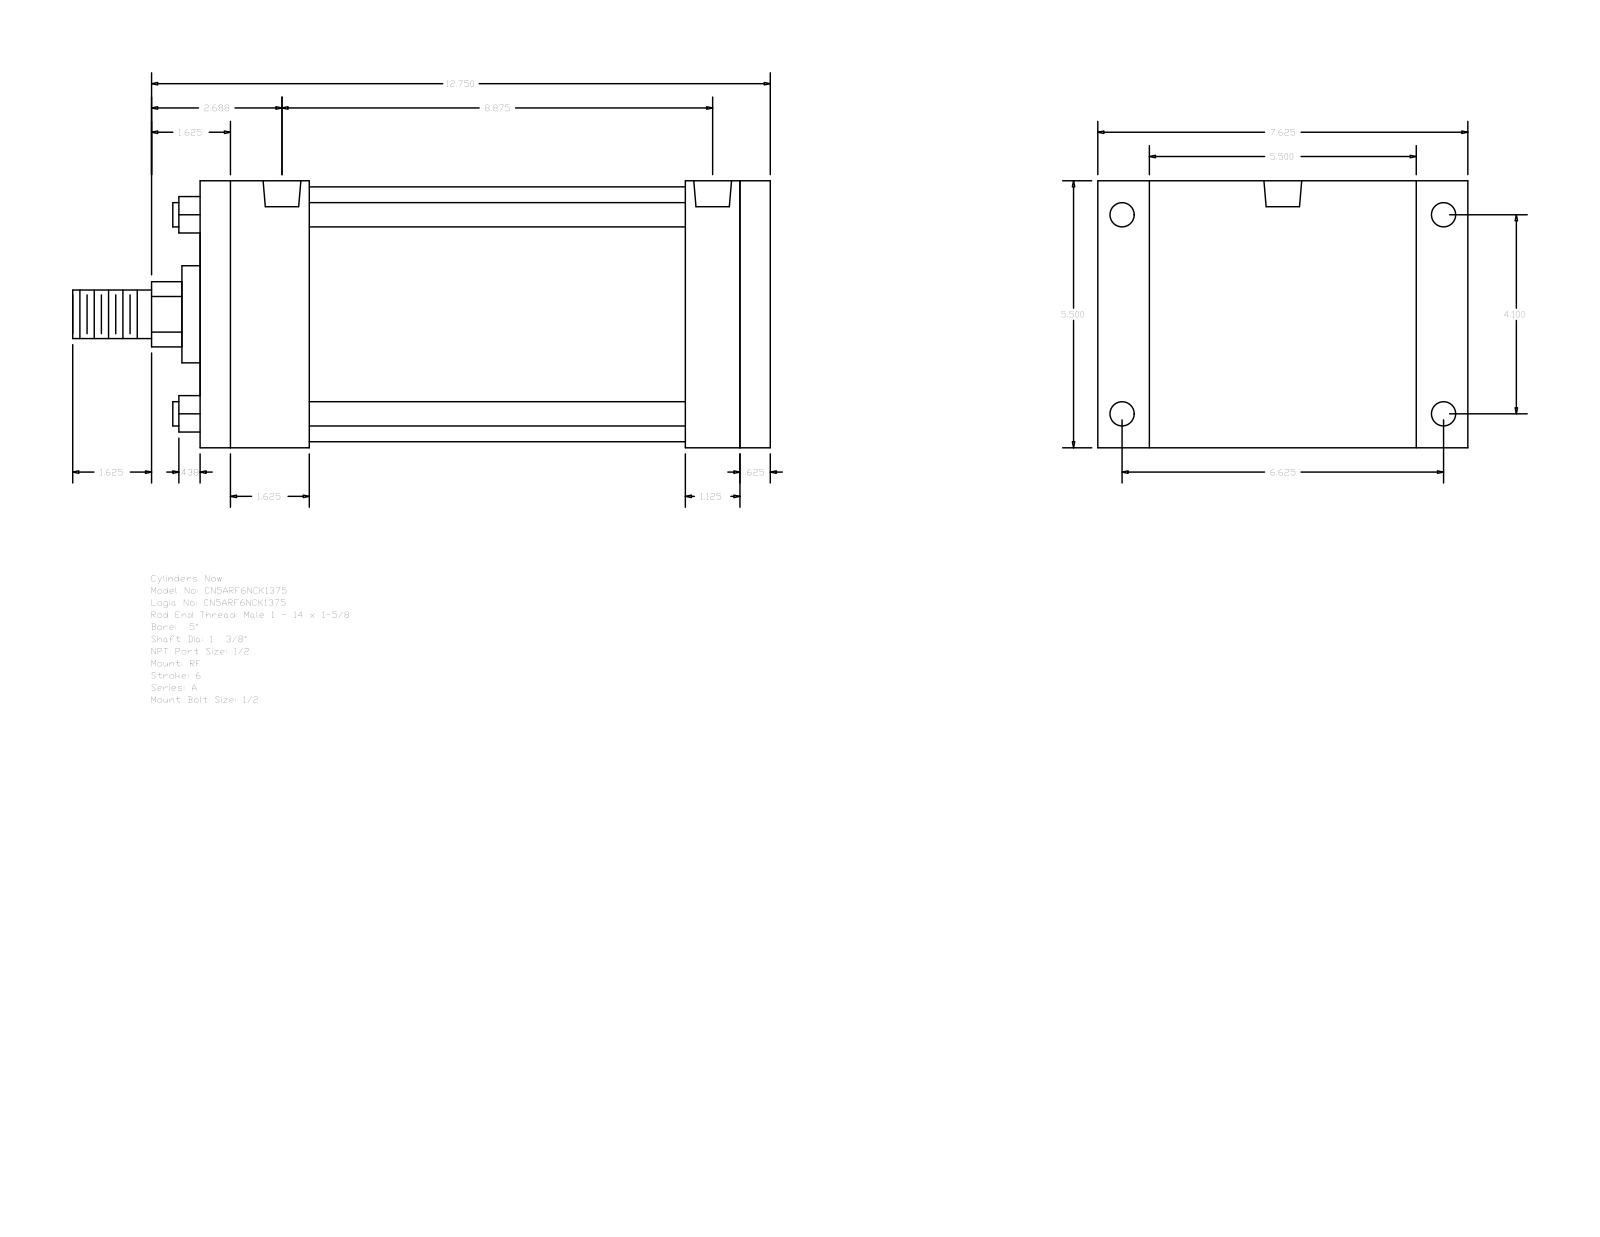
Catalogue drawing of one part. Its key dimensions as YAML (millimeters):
part_name: "A_RF__0500_1.375"
step_written_by: "GSSL Pune (CONFIG_CONTROL_DESIGN)"
units: millimeters
bodies: {solids: 0, faces: 92, planar: 64, cylindrical: 28, other: 0}
overall_size: [365.12, 193.68, 139.7]
round_holes:
  - {diameter: 8.73, count: 4}
  - {diameter: 12.7, count: 4}
  - {diameter: 19.77, count: 2}
round_bosses_or_shafts:
  - {diameter: 12.7, count: 4}
  - {diameter: 133.35, count: 1}
  - {diameter: 50.8, count: 1}
  - {diameter: 34.92, count: 1}
  - {diameter: 25.4, count: 1}
partial_cylinders:
  - {radius: 17.06, count: 1}
face_to_face_distances: [139.7, 298.45, 282.58, 15.87, 57.15, 28.58, 225.43, 241.3, 254, 196.85]
hole_center_spacings: [2.39, 104.14, 168.28, 197.9, 220.65, 223.04, 225.43]
